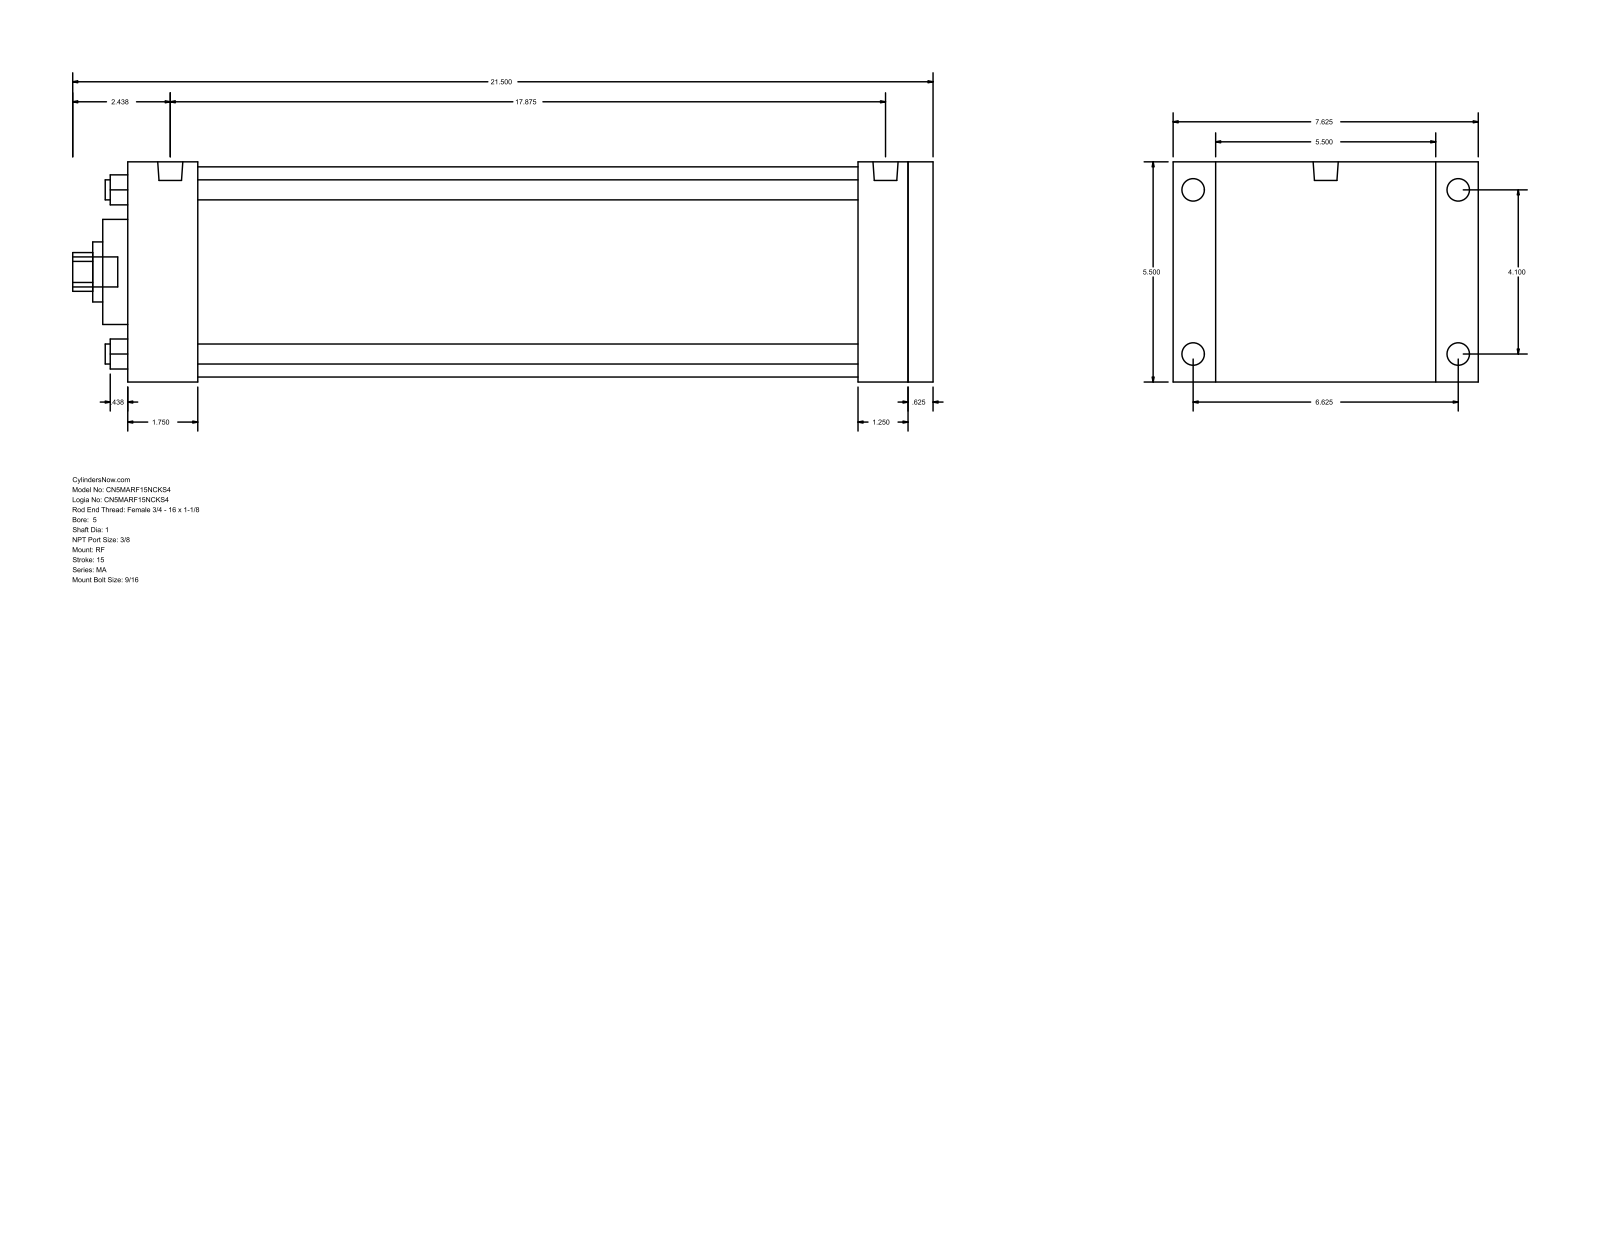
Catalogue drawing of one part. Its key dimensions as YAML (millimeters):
part_name: "MA_RF__0500_1"
step_written_by: "GSSL Pune (CONFIG_CONTROL_DESIGN)"
units: millimeters
bodies: {solids: 0, faces: 94, planar: 65, cylindrical: 29, other: 0}
overall_size: [546.1, 193.68, 139.7]
round_holes:
  - {diameter: 12.7, count: 4}
  - {diameter: 25.4, count: 1}
  - {diameter: 38.1, count: 1}
  - {diameter: 66.67, count: 1}
  - {diameter: 133.35, count: 1}
round_bosses_or_shafts:
  - {diameter: 14.29, count: 4}
  - {diameter: 11.11, count: 4}
  - {diameter: 15.93, count: 2}
  - {diameter: 19.05, count: 1}
partial_cylinders:
  - {radius: 12.29, count: 1}
face_to_face_distances: [139.7, 511.18, 15.87, 495.31, 44.46, 450.85, 466.72, 463.56, 419.1, 31.75]
hole_center_spacings: [73.64, 104.14, 147.28]
